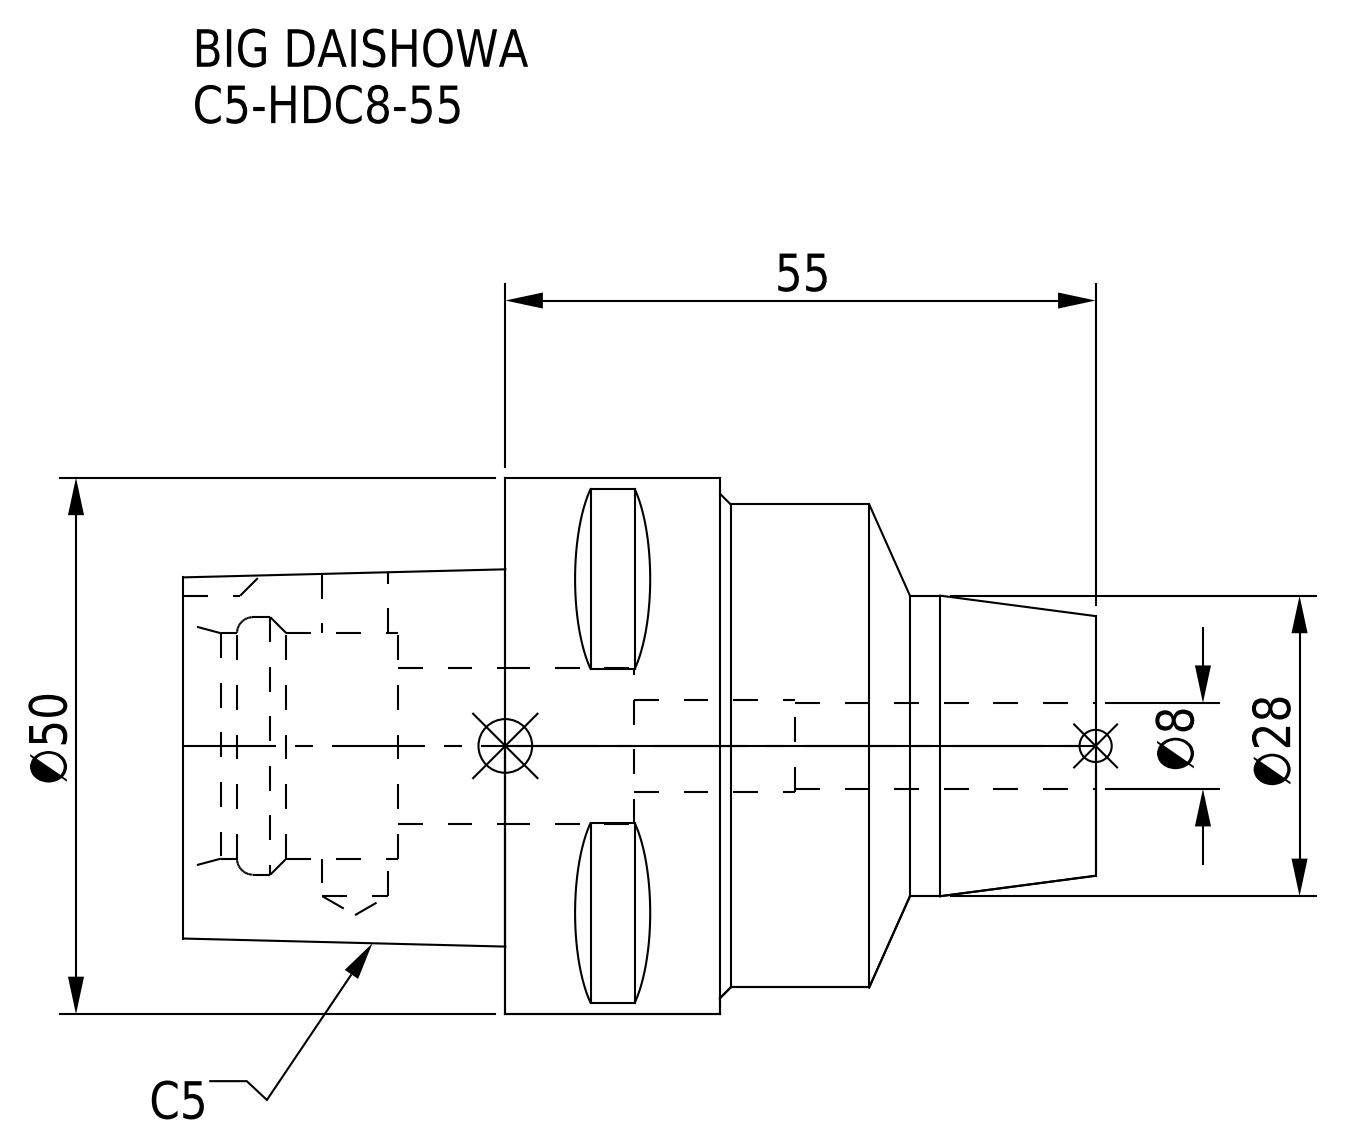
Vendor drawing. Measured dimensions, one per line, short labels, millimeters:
name: C5-HDC8-55
written by: CREO PARAMETRIC BY PTC INC, 2016380 (AUTOMOTIVE_DESIGN)
unit: mm
bodies: 1 solid, 68 faces (29 planar, 23 cylindrical, 16 other)
size: 85 × 50 × 50
volume: 87 958 mm³; area: 17 245 mm²
holes: 1× ⌀6.1, 1× ⌀8, 1× ⌀8.5, 1× ⌀14.5, 1× ⌀21, 1× ⌀24
bosses: 1× ⌀50, 1× ⌀45, 1× ⌀28
rounds: 1× R4
face distances: 30, 20, 55, 85, 35, 50, 44, 65, 10, 19.18
